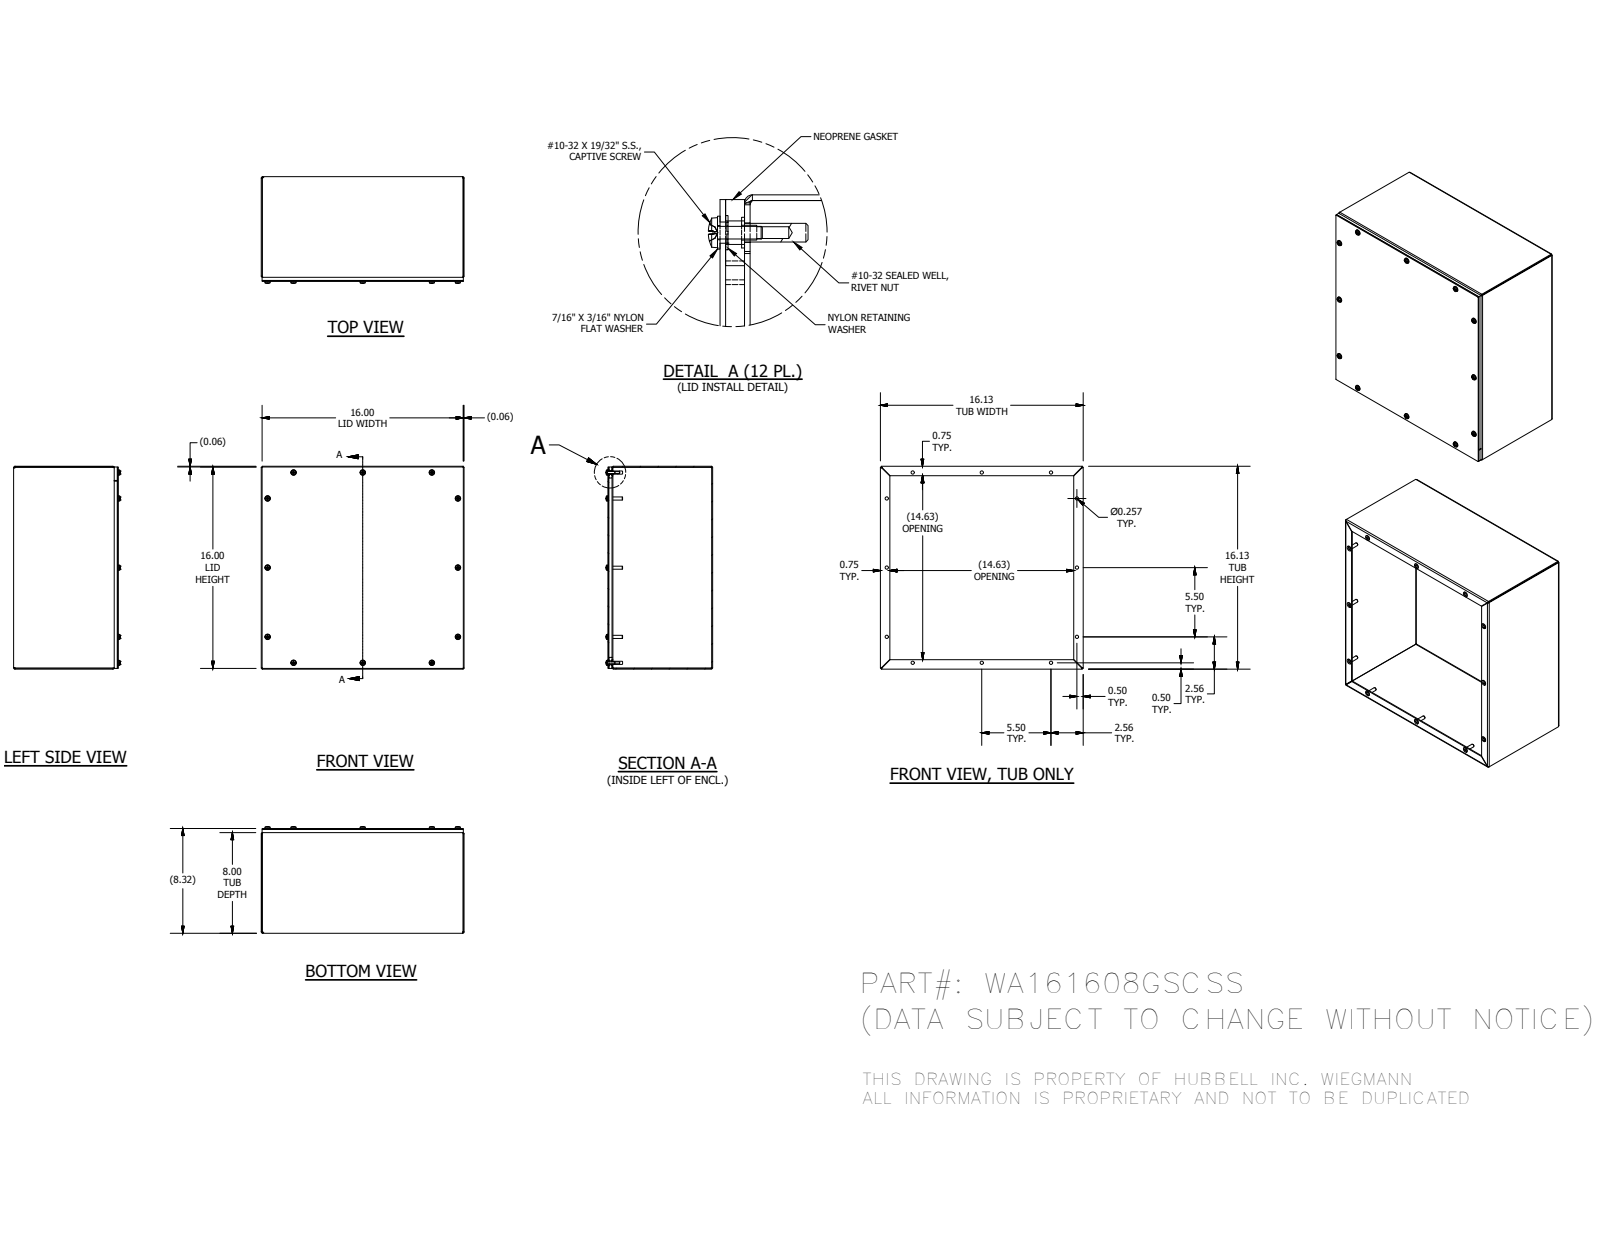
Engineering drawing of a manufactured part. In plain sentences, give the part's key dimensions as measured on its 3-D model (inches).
The part is named "WA161608GSCSSBKP; WA1616GSCSSLID; 37210; 39035 (+4 more)". Its 3-D file was written by "Autodesk Inventor 2016 (AUTOMOTIVE_DESIGN)". It is 52 solids with 1088 faces: 596 planar, 224 cylindrical and 268 other. Overall it measures 16.125 by 16.125 by 8.478 inches. Its volume is 92.08 cubic inches and its surface area 2 303 square inches. Round holes: 12 of diameter 0.156, 12 of diameter 0.188, 12 of diameter 0.196, 12 of diameter 0.257, 12 of diameter 0.278, 12 of diameter 0.281, 12 of diameter 0.313. Round bosses or shafts: 12 of diameter 0.453, 12 of diameter 0.437, 12 of diameter 0.406, 12 of diameter 0.248, 12 of diameter 0.167. Partial cylindrical surfaces (rounded edges, fillets, slot ends): 12 of radius 0.031, 12 of radius 0.089, 8 of radius 0.07, 8 of radius 0.105. The main face-to-face distances are 0.074, 8.25, 16.051, 8.324, 8.176, 16.125, 15.977, 7.926, 0.324, 0.25. The hole center spacings are 5.5, 11, 13.224, 13.224, 15.093, 16.093, 15.124, 2.917.
